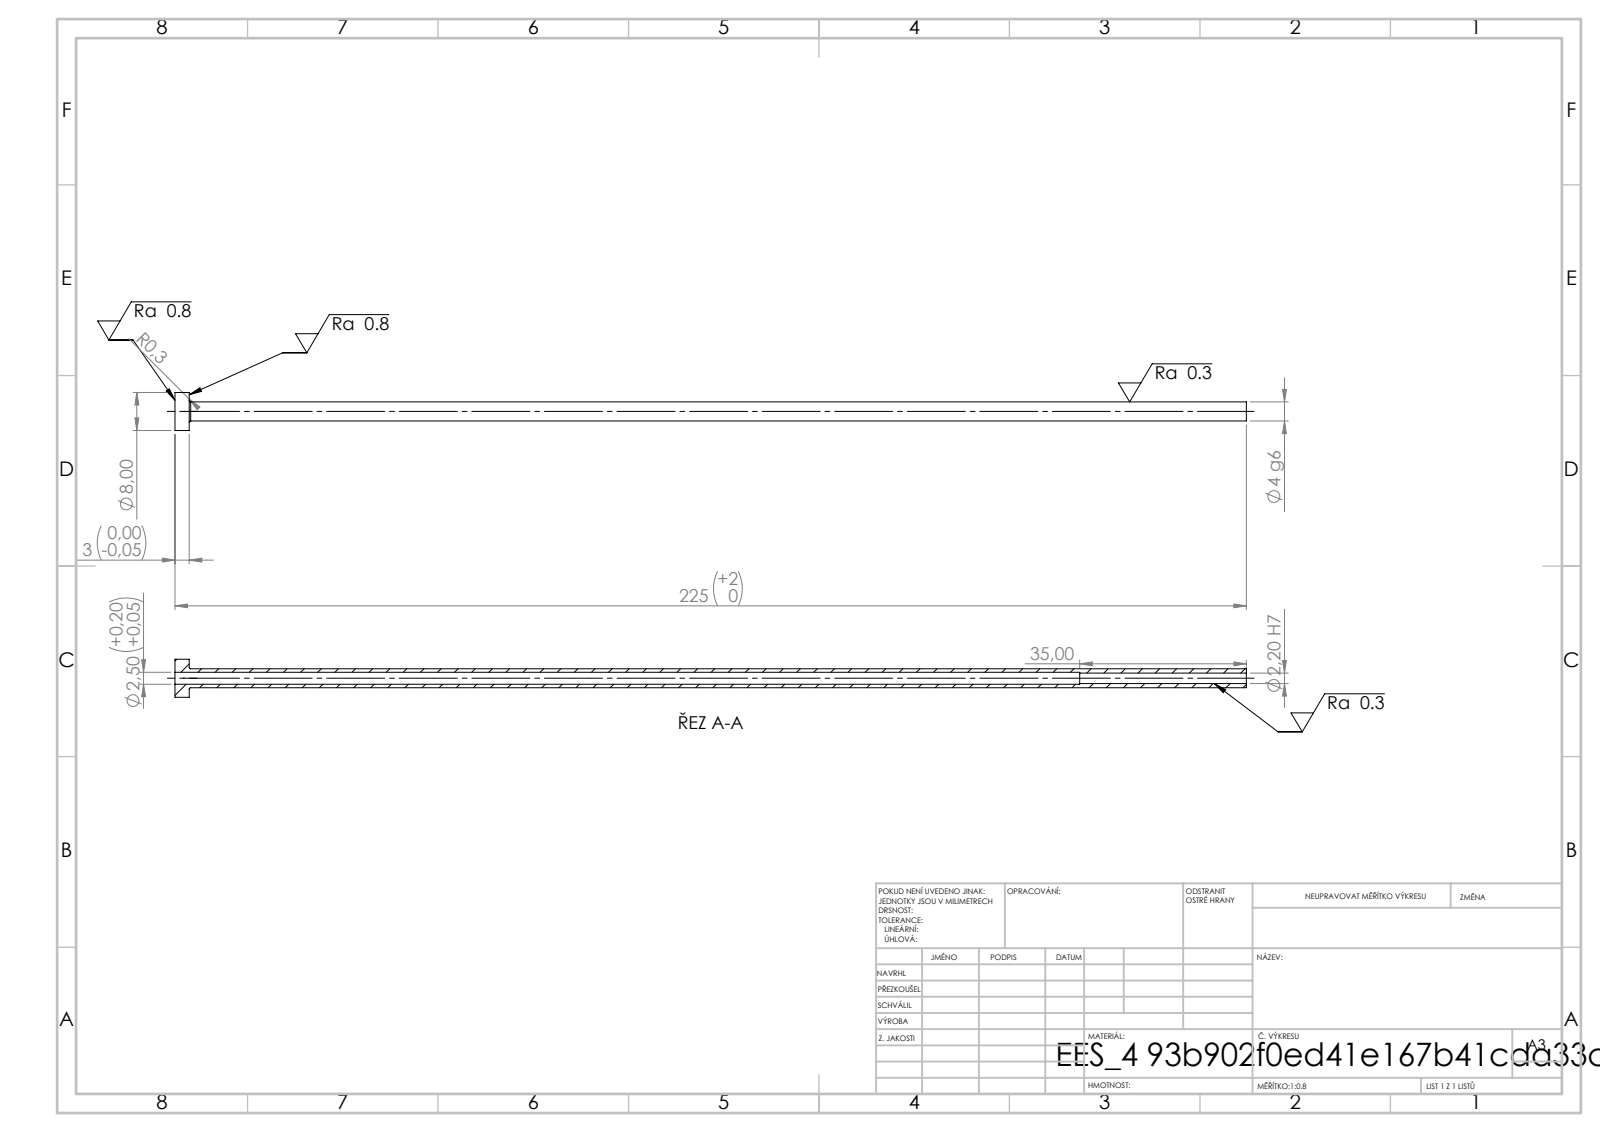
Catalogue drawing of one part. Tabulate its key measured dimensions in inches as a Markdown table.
| quantity | value |
| --- | --- |
| STEP written by | SolidWorks 2019 (CONFIG_CONTROL_DESIGN) |
| units | inches |
| bodies | 1 solid, 14 faces (4 planar, 8 cylindrical, 2 other) |
| overall size | 8.858 × 0.315 × 0.315 |
| volume | 0.114 in³ |
| surface area | 7.271 in² |
| round holes (diameter × count) | 0.087 × 1, 0.098 × 1 |
| round bosses / shafts (diameter × count) | 0.315 × 1, 0.157 × 1 |
| main face-to-face distances | 0.118, 8.858, 8.74, 7.48, 7.362, 1.378 |
